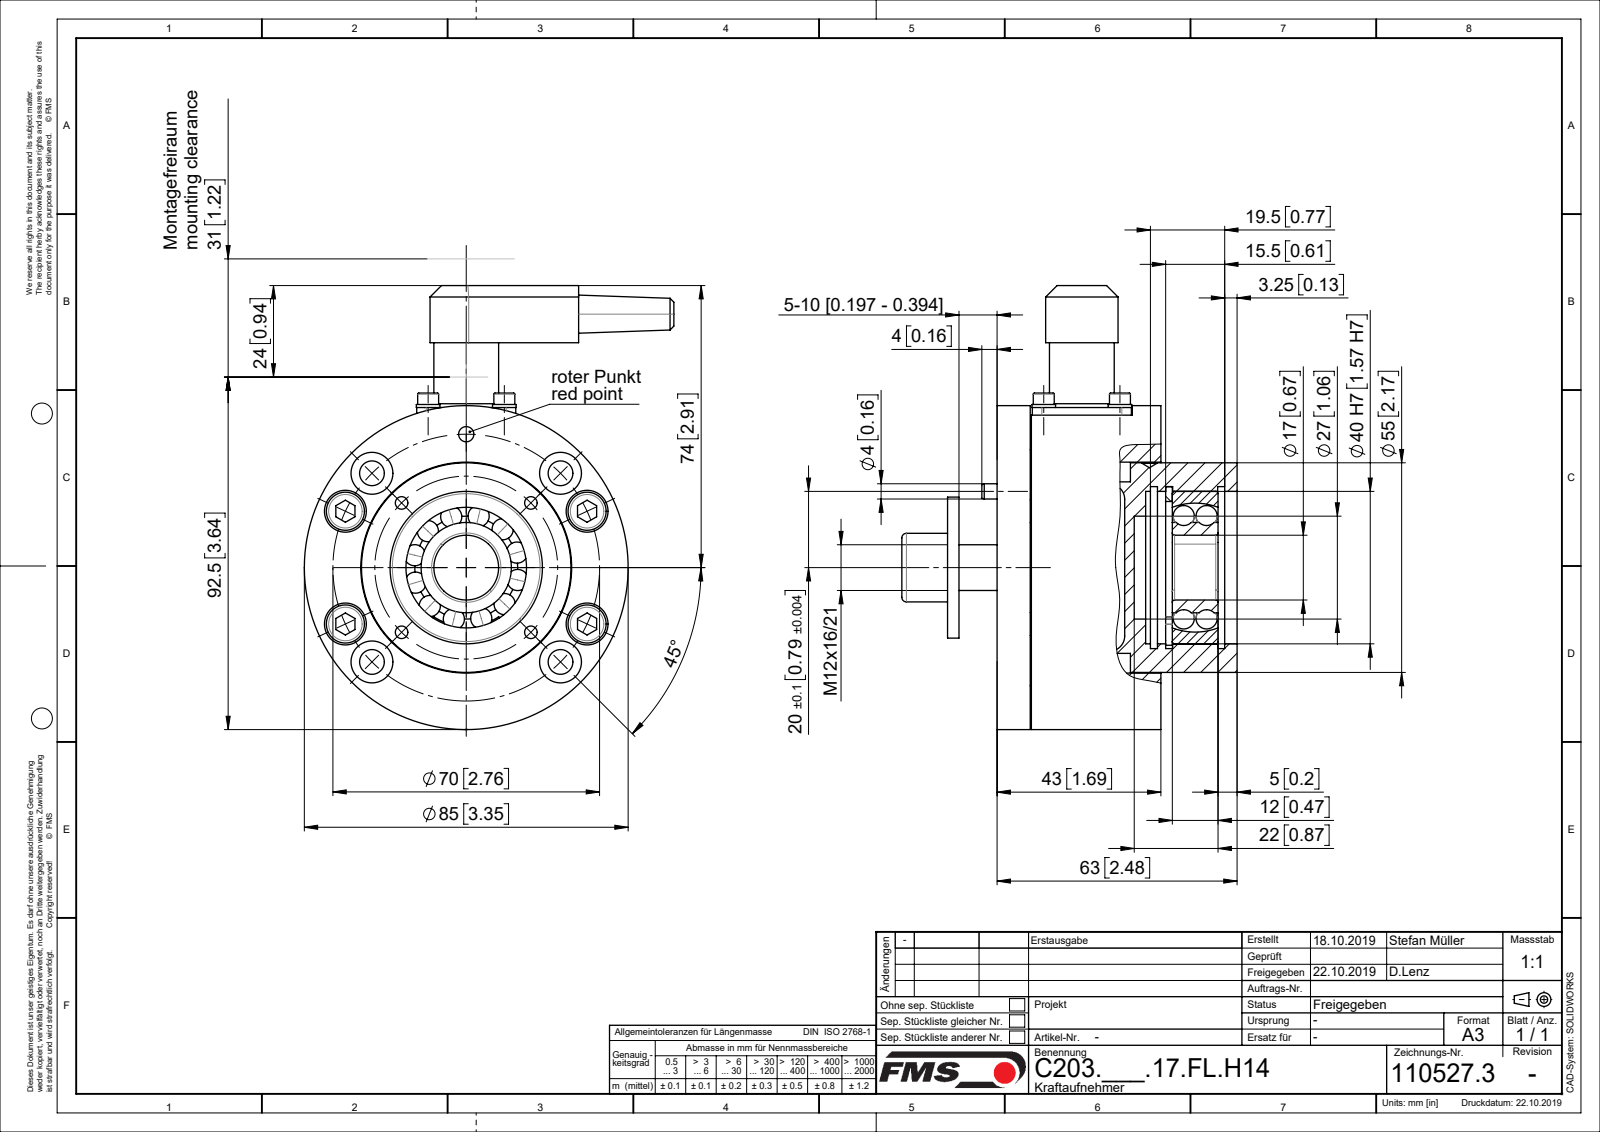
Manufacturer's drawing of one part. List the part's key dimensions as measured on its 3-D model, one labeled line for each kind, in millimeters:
Part name (STEP PRODUCT): ZEICHNUNG3; C1105273; C1105271; C0704203 (+8 more)
STEP written by: Mechanical Desktop 2009 (CONFIG_CONTROL_DESIGN)
Units: millimetres
Bodies: 24 solids, 472 faces (149 planar, 240 cylindrical, 83 other)
Overall size (bounding box): 116.5 × 97 × 67
Volume: 255 218 mm³ · Surface area: 83 398 mm²
Round holes (diameter × count): ⌀6.5 ×8, ⌀11 ×8, ⌀2 ×5, ⌀2.6 ×4, ⌀3.2 ×4, ⌀3.42 ×4, ⌀5.15 ×4, ⌀7 ×4, ⌀4 ×1, ⌀10.68 ×1, ⌀12 ×1, ⌀15 ×1
Round bosses / shafts (diameter × count): ⌀1.5 ×5, ⌀10 ×4, ⌀6.2 ×4, ⌀6 ×4, ⌀5.5 ×4, ⌀5 ×4, ⌀3 ×4, ⌀85 ×1
Partial cylindrical surfaces — rounded edges, fillets, slot ends (radius × count): R2.5 ×4, R5 ×2, R9.5 ×1
Main face-to-face distances: 3, 8.7, 34, 42.7, 6, 43, 15, 4, 9, 33
Hole centre spacings: 35, 42.44, 20, 11, 12.16, 14.14, 14.91, 24
